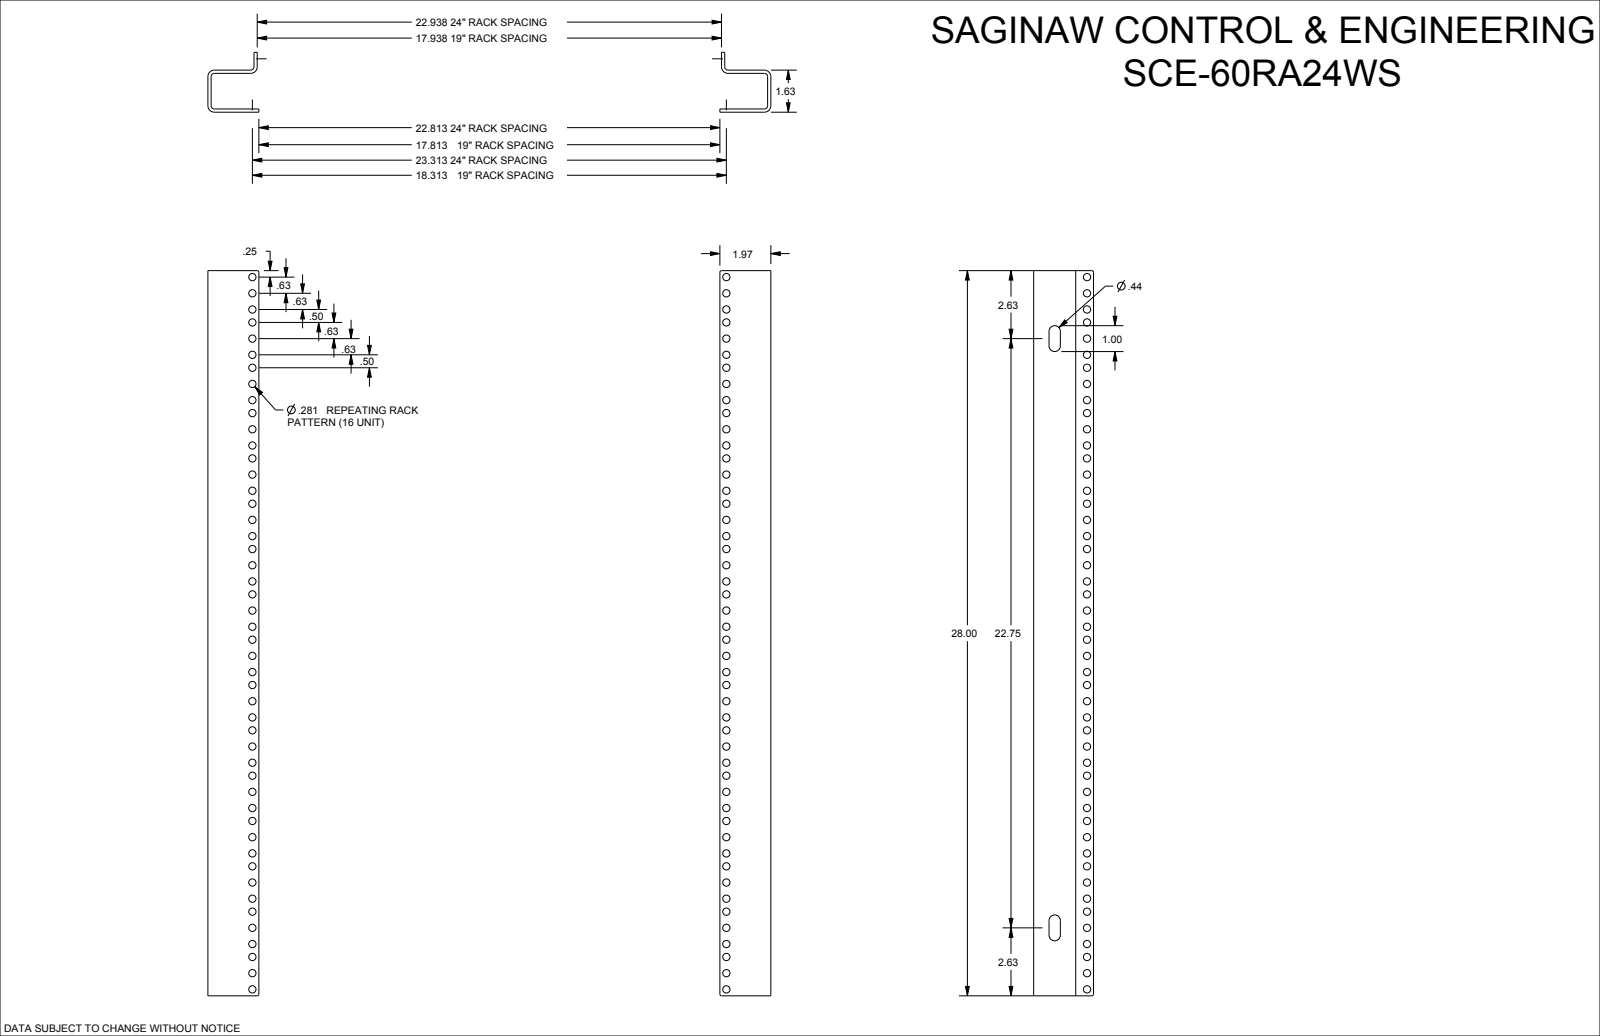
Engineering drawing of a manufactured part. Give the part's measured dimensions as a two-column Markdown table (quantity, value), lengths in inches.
| quantity | value |
| --- | --- |
| part name | SCE-60RA24WS |
| STEP written by | SolidWorks 2019 (CONFIG_CONTROL_DESIGN) |
| units | inches |
| bodies | 2 solids, 252 faces (32 planar, 220 cylindrical, 0 other) |
| overall size | 28 × 26.751 × 2.312 |
| volume | 38.18 in³ |
| surface area | 650.2 in² |
| round holes (diameter × count) | 0.281 × 146 |
| partial cylindrical surfaces (radius × count) | 0.062 × 6, 0.125 × 6, 0.25 × 6, 0.219 × 4 |
| main face-to-face distances | 0.125, 0.125, 1.5, 1.375, 1.625, 1.5, 24.844, 26.75, 26.625, 26.5 |
| hole center spacings | 1.75, 3.5, 5.25, 7, 8.75, 0.625, 0.625, 1.25 |
